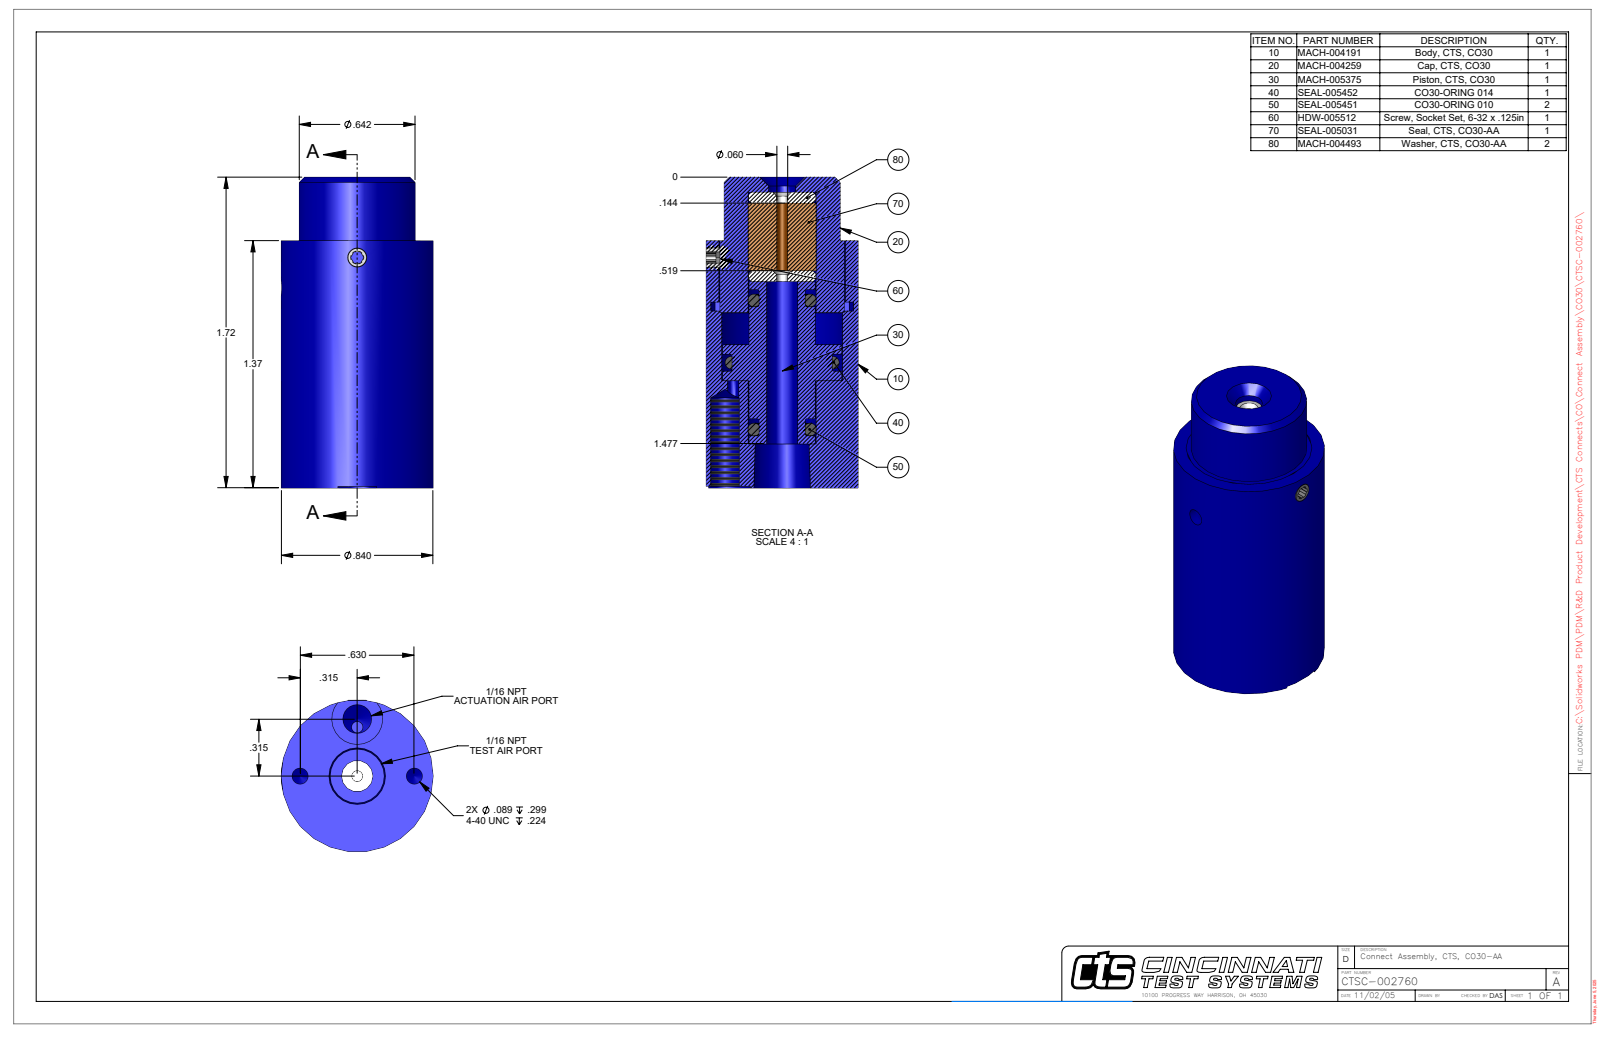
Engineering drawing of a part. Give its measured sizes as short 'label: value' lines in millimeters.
name: CTSC-002760
written by: SolidWorks 2023 (AUTOMOTIVE_DESIGN)
unit: mm
bodies: 1 solid, 138 faces (69 planar, 47 cylindrical, 22 other)
size: 43.7 × 21.3 × 21.3
volume: 13 500 mm³; area: 4 350 mm²
holes: 2× ⌀2.3, 1× ⌀1.5, 1× ⌀1.6, 1× ⌀2.4, 1× ⌀2.7, 1× ⌀3.8, 1× ⌀4, 1× ⌀4.4, 1× ⌀17.7
bosses: 1× ⌀21.3, 1× ⌀16.3
rounds: 1× R0.8, 1× R0.9, 1× R3.6, 1× R10.5
face distances: 43.7, 34.8, 8.9, 6.2, 28.6, 37.5, 34.8, 28.5, 9, 17.4
hole spacings: 8, 11.3, 16
